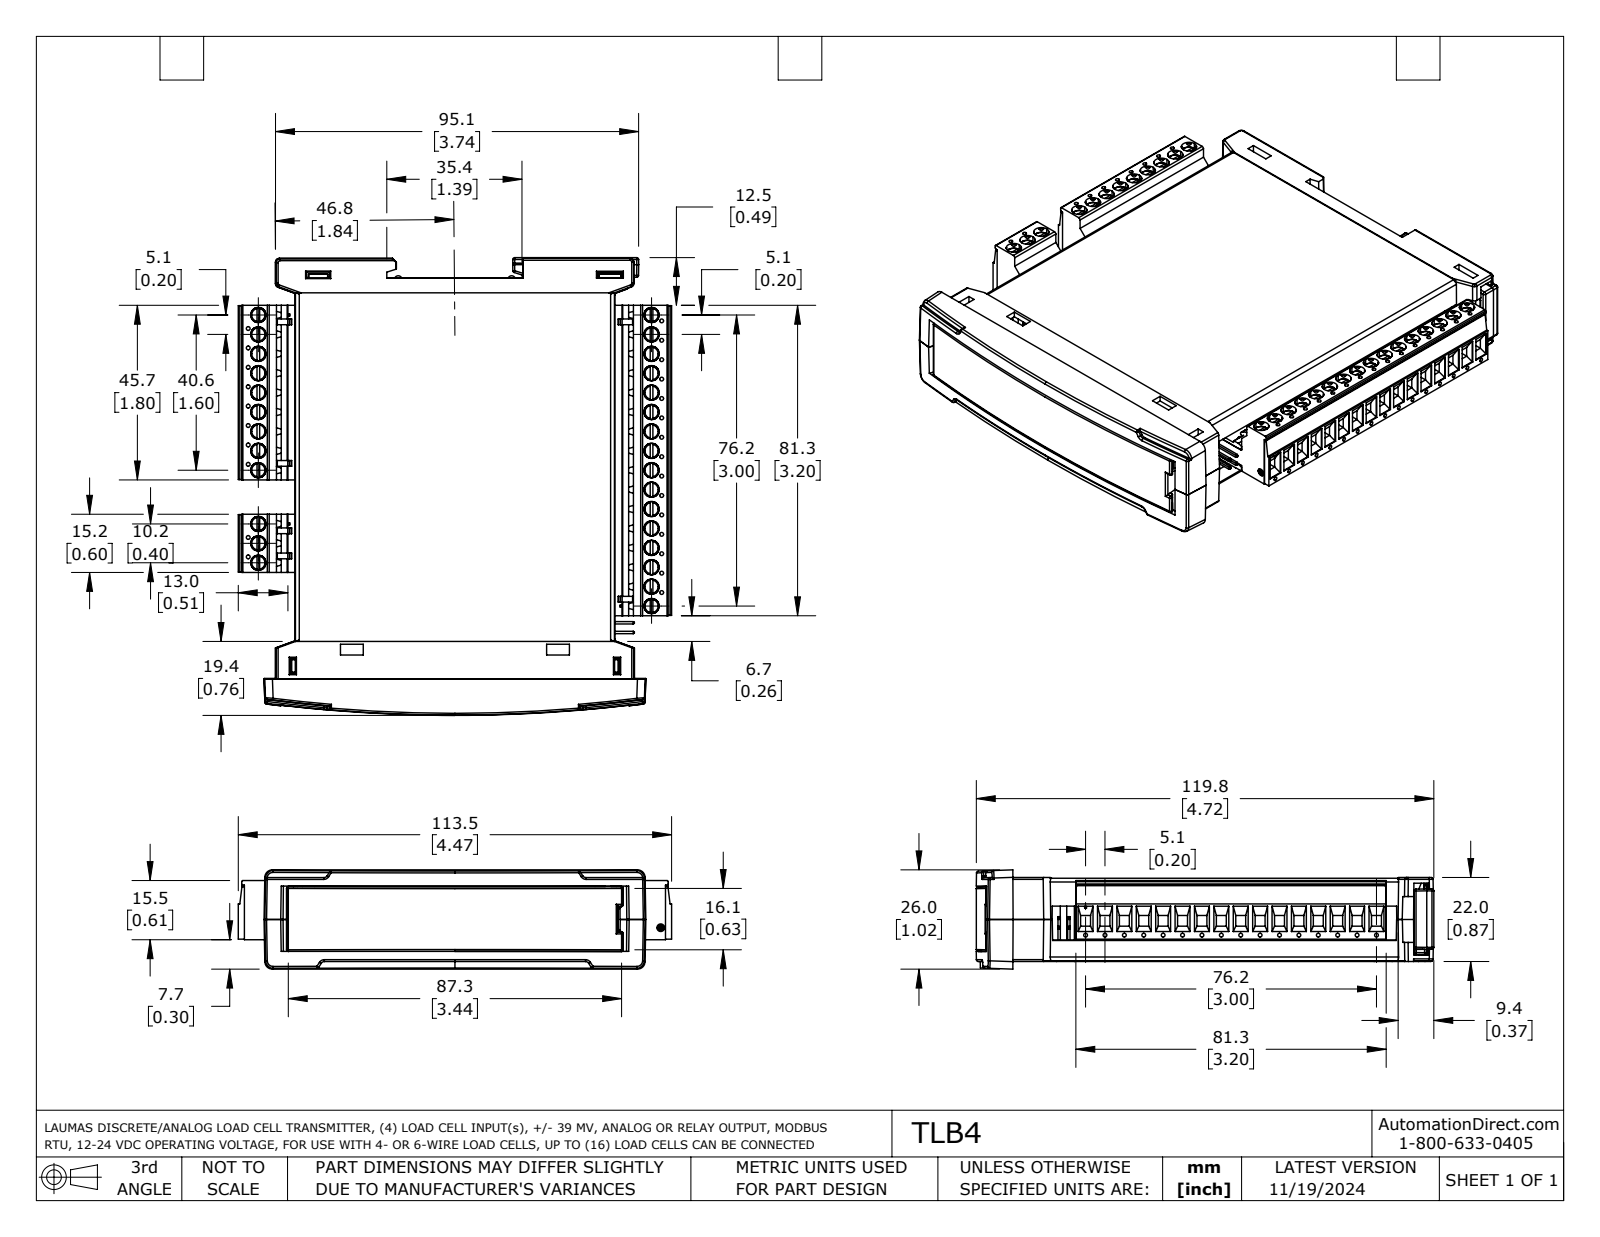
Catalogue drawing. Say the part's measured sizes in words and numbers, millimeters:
The part is named "TLB4". Its 3-D file was written by "SolidWorks 2021 (AUTOMOTIVE_DESIGN)". It is 21 solids with 6235 faces: 3961 planar, 1607 cylindrical and 667 other. Overall it measures 119.9 by 113.5 by 26 millimeters. Its volume is 85 570 cubic millimeters and its surface area 111 500 square millimeters. Round holes: 63 of diameter 1, 28 of diameter 4, 19 of diameter 1.5, 19 of diameter 3.7, 6 of diameter 0.7, 6 of diameter 2, 4 of diameter 0.9, 3 of diameter 1.7. Round bosses or shafts: 28 of diameter 3.9, 28 of diameter 1.4, 19 of diameter 2.7, 4 of diameter 2.9, 3 of diameter 1.3, 2 of diameter 1.5, 1 of diameter 2.4. Partial cylindrical surfaces (rounded edges, fillets, slot ends): 157 of radius 0.5, 116 of radius 0.1, 76 of radius 0.1, 26 of radius 1, 22 of radius 0.3, 19 of radius 1.8, 19 of radius 3, 19 of radius 3.1. The main face-to-face distances are 1.3, 20.3, 4.1, 1.5, 14.9, 16.5, 19, 2.5, 1.6, 17.8. The hole center spacings are 5.1, 10.2, 5.6, 2.4, 15.2, 20.3, 10.4, 25.4.
